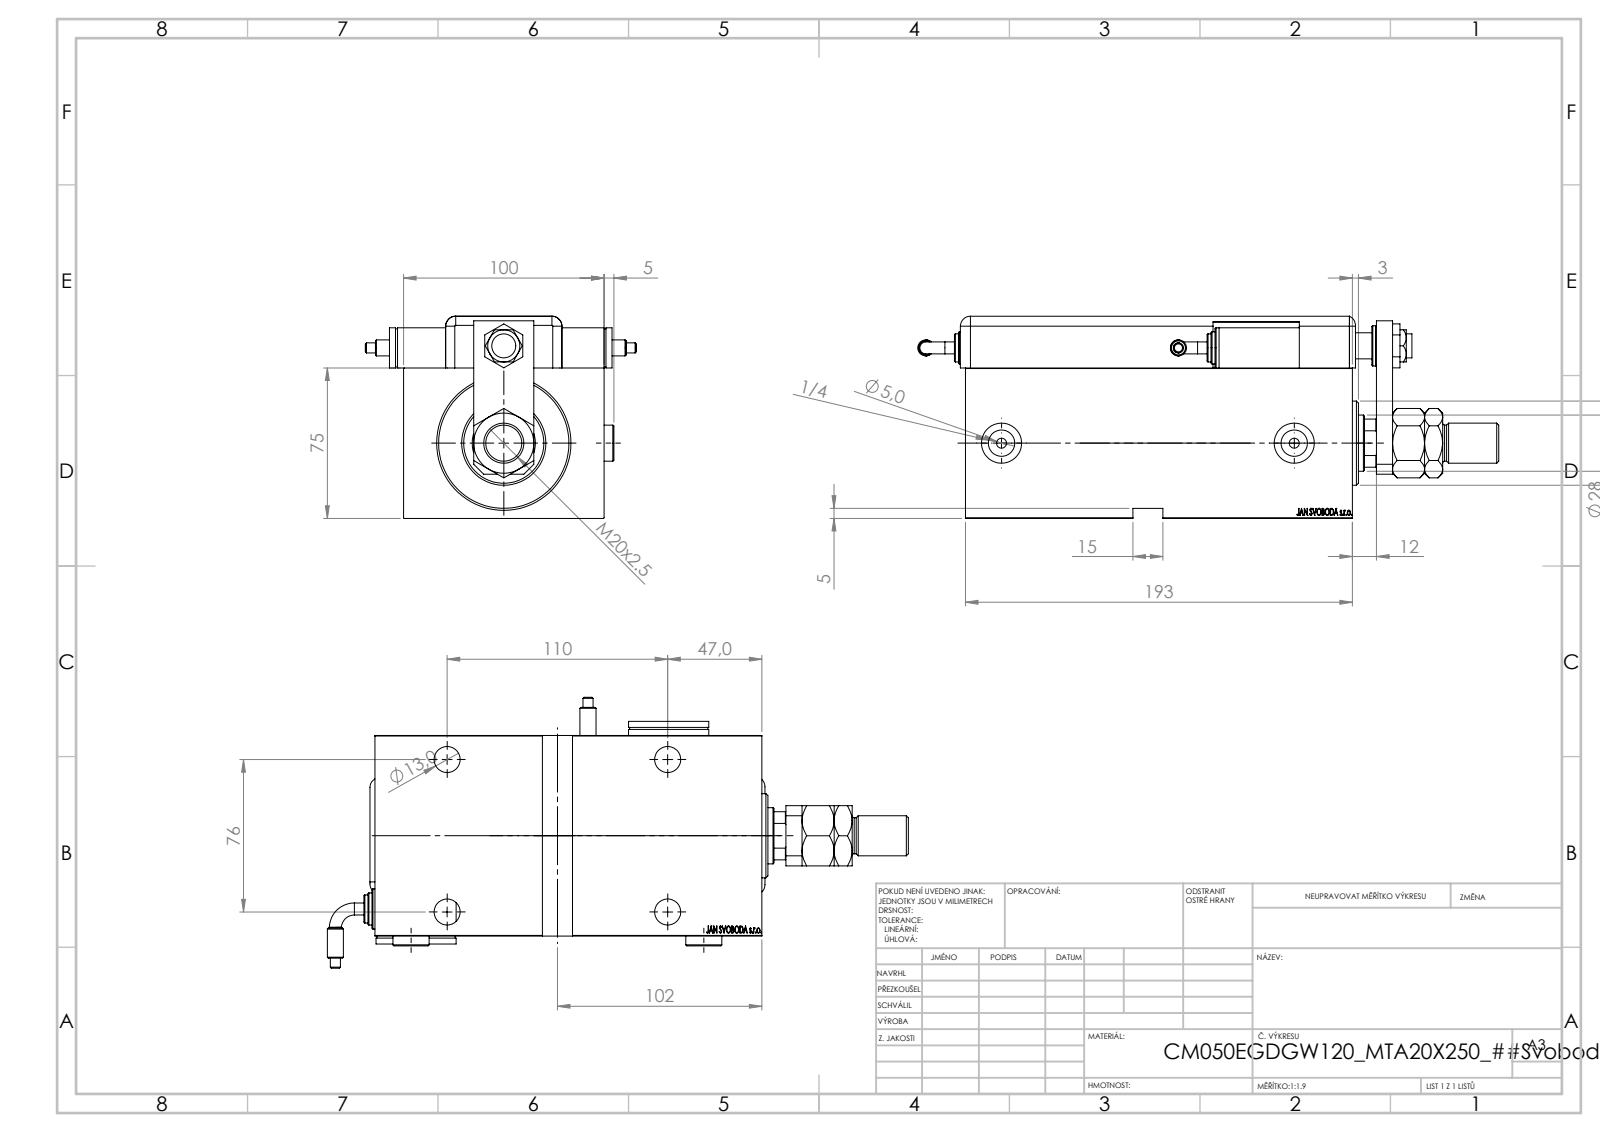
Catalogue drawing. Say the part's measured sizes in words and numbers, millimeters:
The part is named "SWITCH_Q_FRONT_BACK; ZARAZKA_Q; Q_T_W_MTA; V450CM_VC_B (+7 more)". Its 3-D file was written by "SolidWorks 2019 (CONFIG_CONTROL_DESIGN)". It is 16 solids with 1373 faces: 671 planar, 135 cylindrical and 567 other. Overall it measures 289.76 by 135.01 by 100.8 millimeters. Its volume is 1 444 000 cubic millimeters and its surface area 249 330 square millimeters. Round holes: 5 of diameter 13, 4 of diameter 19, 3 of diameter 20, 2 of diameter 4, 2 of diameter 5, 2 of diameter 8, 2 of diameter 13.16, 1 of diameter 12, 1 of diameter 14, 1 of diameter 18.5, 1 of diameter 28, 1 of diameter 31.5. Round bosses or shafts: 3 of diameter 20, 3 of diameter 18, 2 of diameter 16, 2 of diameter 14, 2 of diameter 8, 2 of diameter 6, 2 of diameter 5.04, 1 of diameter 52. Partial cylindrical surfaces (rounded edges, fillets, slot ends): 9 of radius 5, 1 of radius 10, 1 of radius 13.5. The main face-to-face distances are 75, 3, 100, 100.8, 25.8, 22.8, 97.8, 21, 79, 14. The hole center spacings are 47.2, 61.22, 76, 110, 133.7, 150.63, 155.59, 20.
